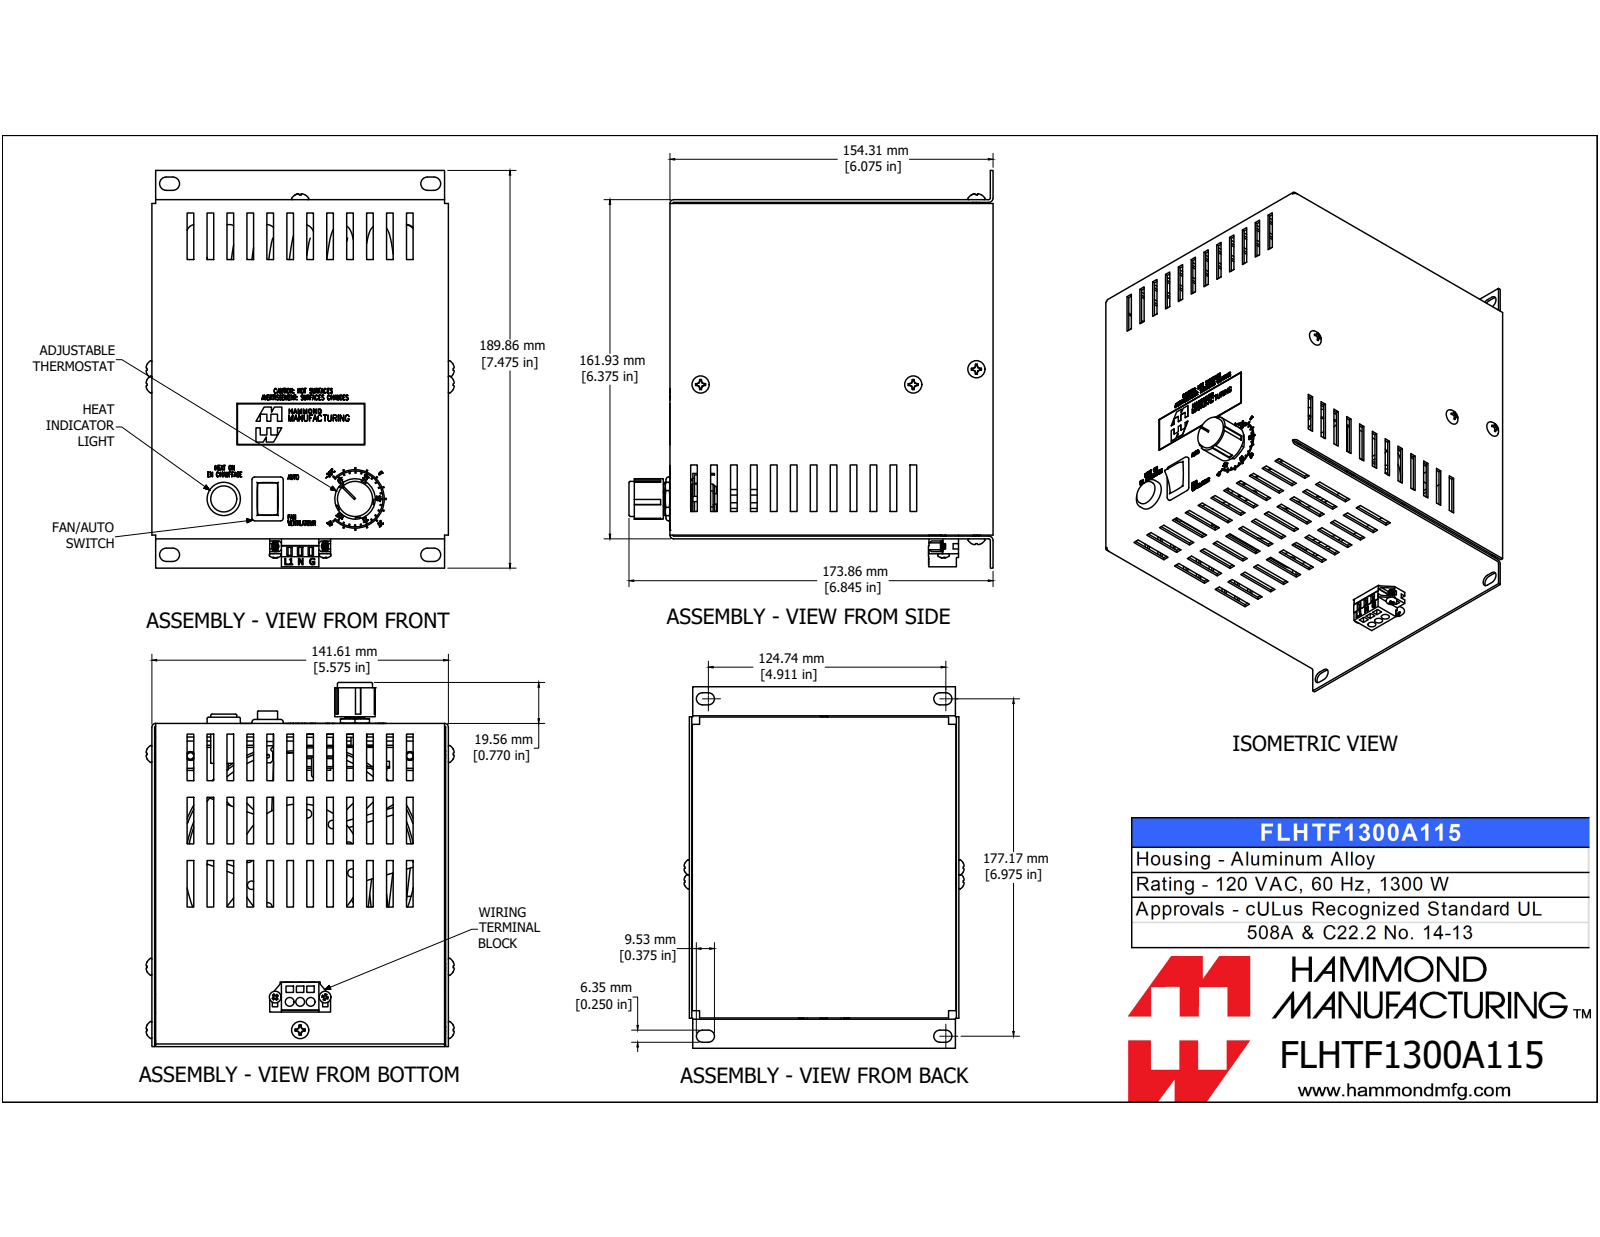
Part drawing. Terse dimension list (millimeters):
name: FLHTF1300A115
written by: SolidWorks 2019 (AUTOMOTIVE_DESIGN)
unit: mm
bodies: 18 solids, 4516 faces (3919 planar, 311 cylindrical, 286 other)
size: 189.9 × 173.9 × 147.1
volume: 343 300 mm³; area: 388 300 mm²
holes: 4× ⌀3.3, 4× ⌀3.5, 4× ⌀4.2, 4× ⌀4.6, 4× ⌀5.2, 3× ⌀4.2, 2× ⌀2.2, 2× ⌀3, 2× ⌀3.3, 2× ⌀4.8, 1× ⌀1.5, 1× ⌀1.7
bosses: 4× ⌀5.5, 4× ⌀4.2, 4× ⌀2.6, 2× ⌀4.3, 2× ⌀2.7, 1× ⌀113, 1× ⌀59, 1× ⌀19.3
rounds: 38× R3.2, 17× R1.3, 12× R16, 9× R3.8, 8× R0.6, 6× R2, 4× R0.5, 4× R1.8
face distances: 1.3, 140.3, 2.5, 160.6, 1.3, 141.6, 139, 152.8, 154.1, 150.3
hole spacings: 5, 7.3, 12, 12.1, 14.4, 14.4, 17.1, 19.7
